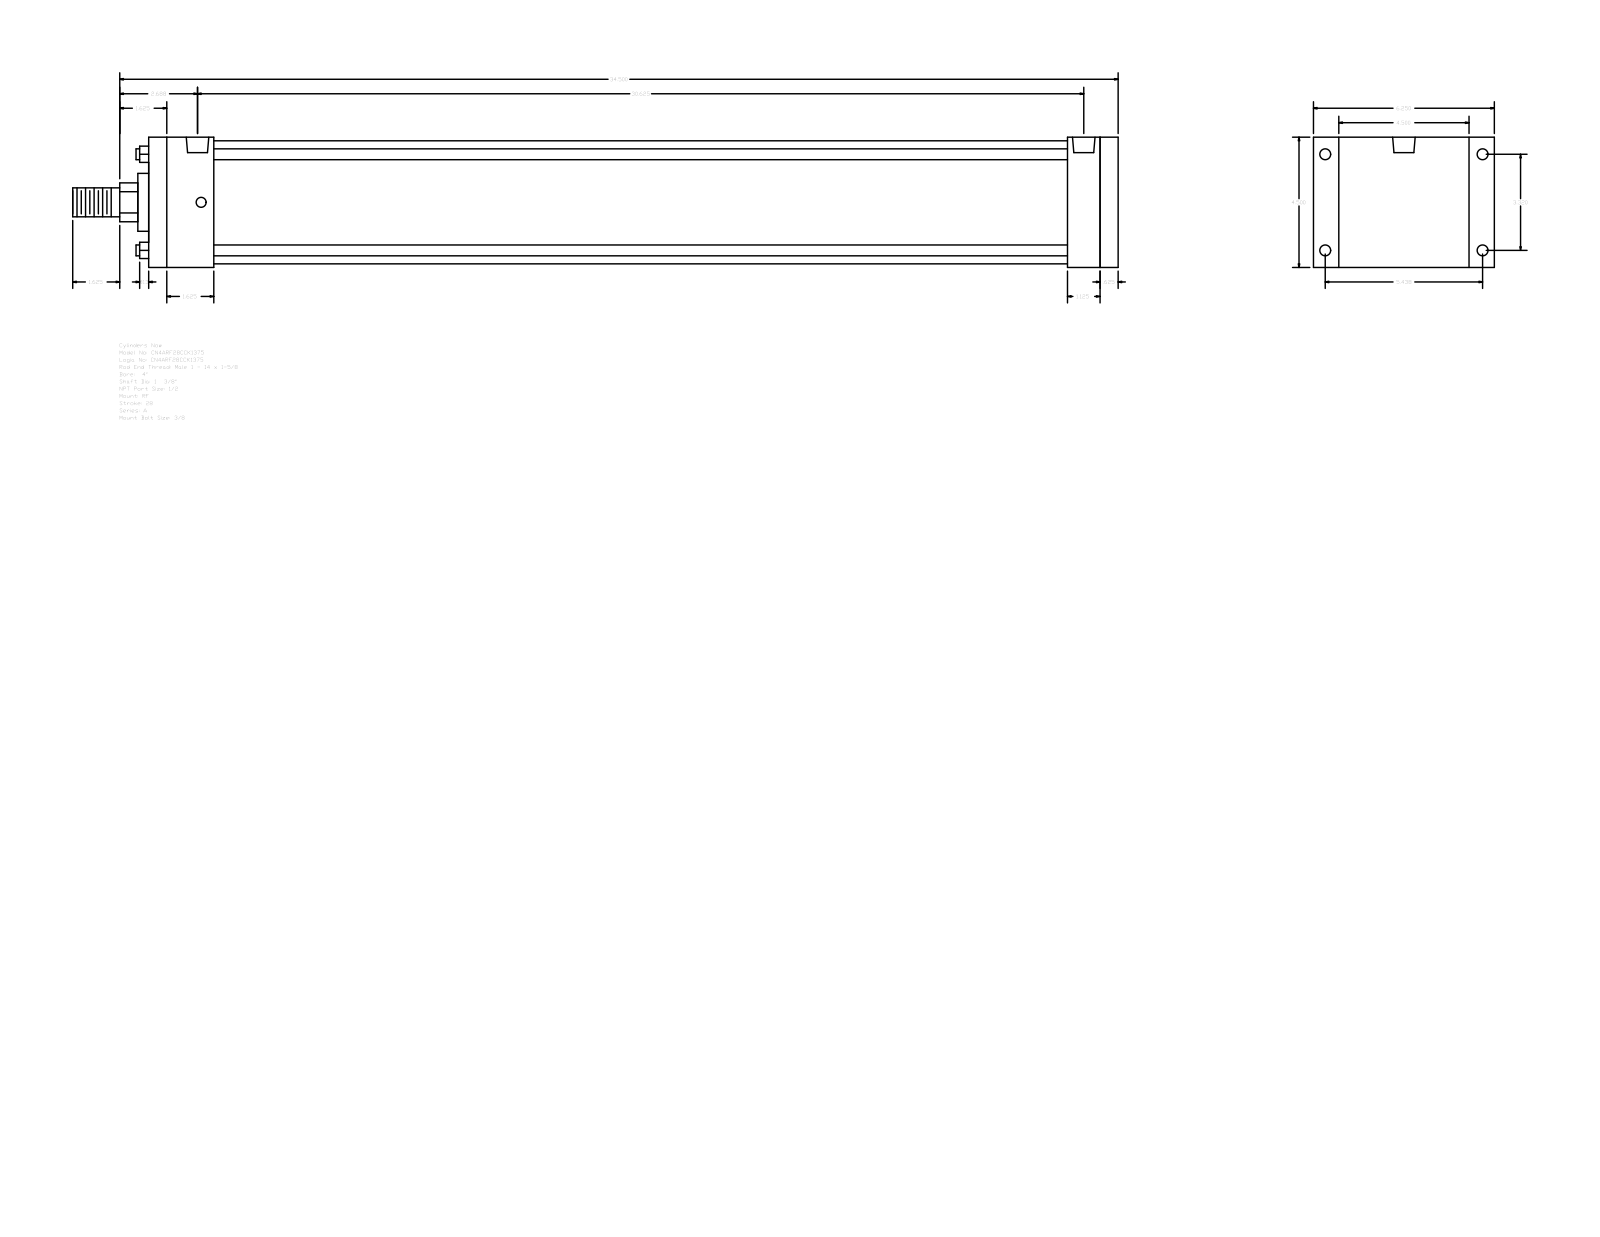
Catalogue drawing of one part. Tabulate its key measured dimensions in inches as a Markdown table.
| quantity | value |
| --- | --- |
| part name | A_RF__0400_1.375 |
| STEP written by | GSSL Pune (CONFIG_CONTROL_DESIGN) |
| units | inches |
| bodies | 0 solids, 92 faces (64 planar, 28 cylindrical, 0 other) |
| overall size | 36.125 × 6.25 × 4.5 |
| round holes (diameter × count) | 0.344 × 4, 0.375 × 4, 0.778 × 2 |
| round bosses / shafts (diameter × count) | 0.375 × 4, 4.25 × 1, 2 × 1, 1.375 × 1, 1 × 1 |
| partial cylindrical surfaces (radius × count) | 0.672 × 1 |
| main face-to-face distances | 4.5, 33.5, 0.625, 32.875, 2.25, 0.875, 5.375, 31.75, 1.125, 1.75 |
| hole center spacings | 0.125, 3.32, 5.438, 6.371, 30.375, 30.5, 30.625 |
